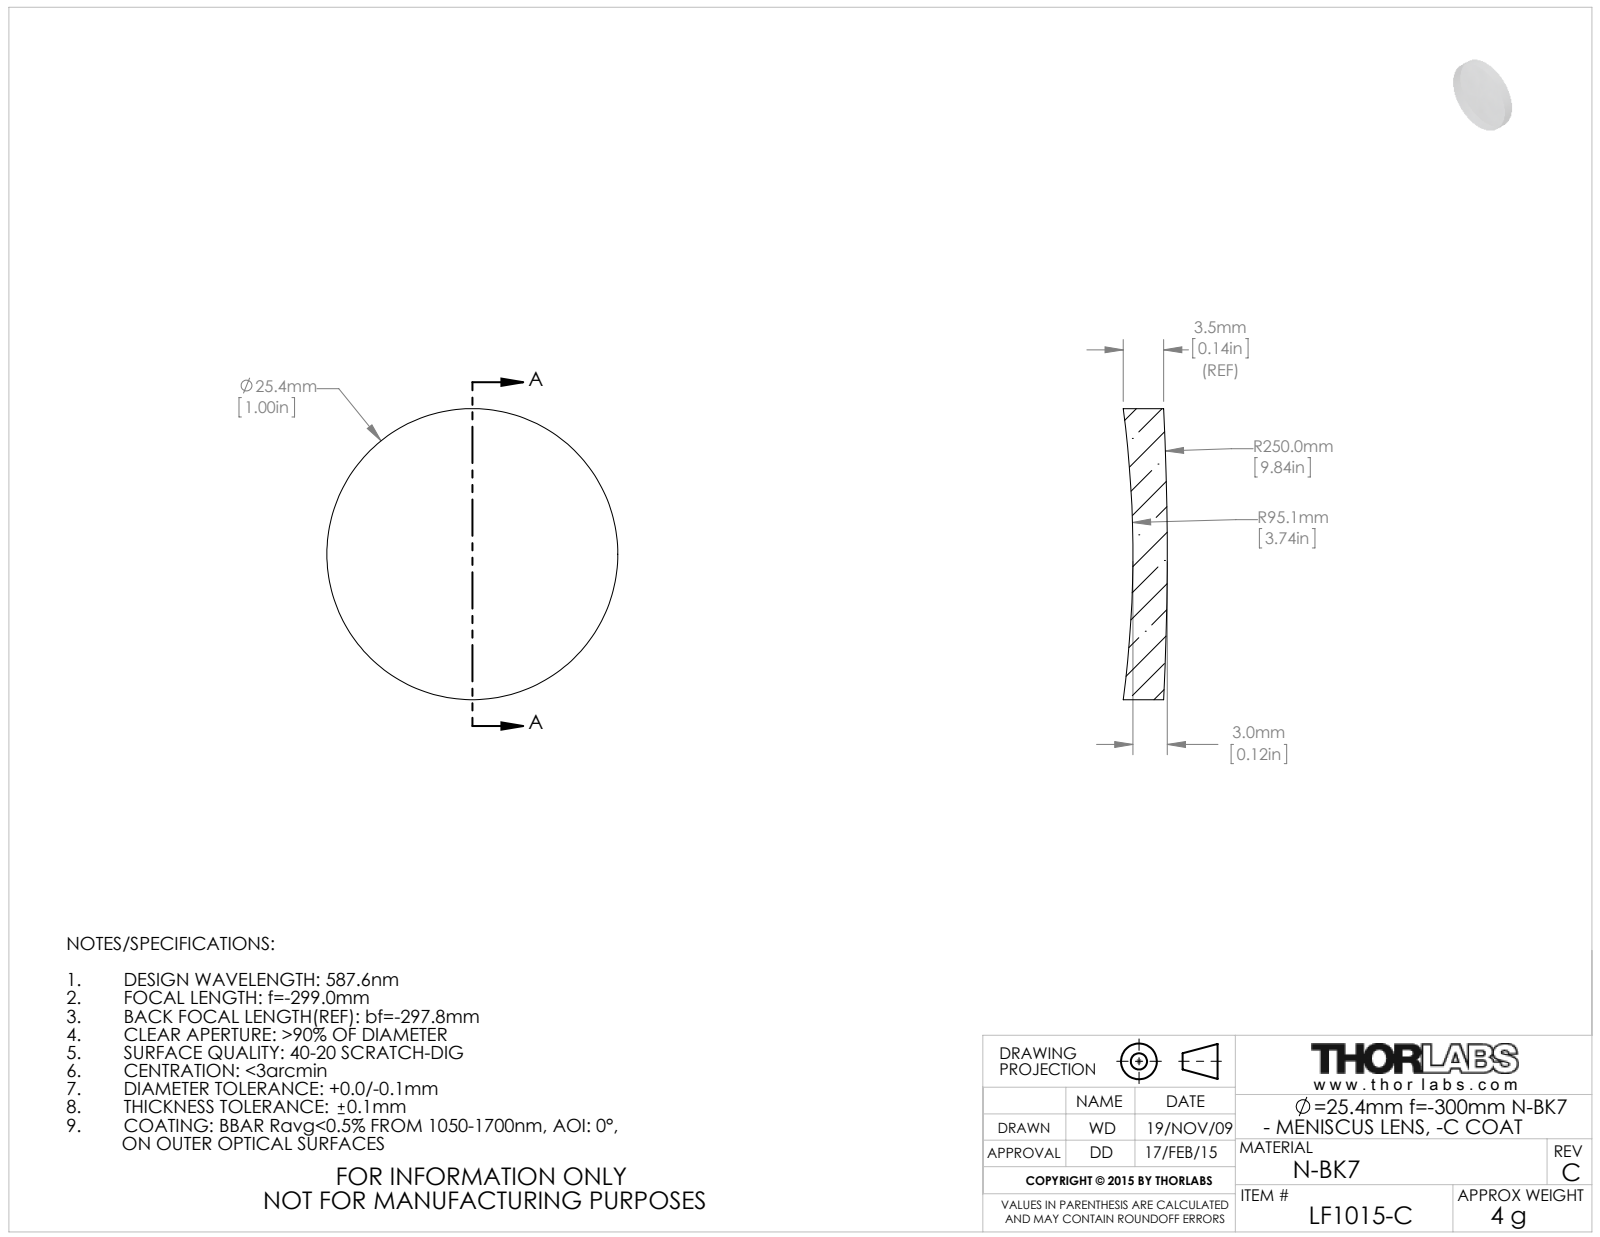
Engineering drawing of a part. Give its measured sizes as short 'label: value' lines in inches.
name: 4910-E0W
written by: SolidWorks 2009 (AUTOMOTIVE_DESIGN)
unit: in
bodies: 1 solid, 6 faces (0 planar, 2 cylindrical, 4 other)
size: 1 × 1 × 0.152
volume: 0.101 in³; area: 2.012 in²
bosses: 1× ⌀1
